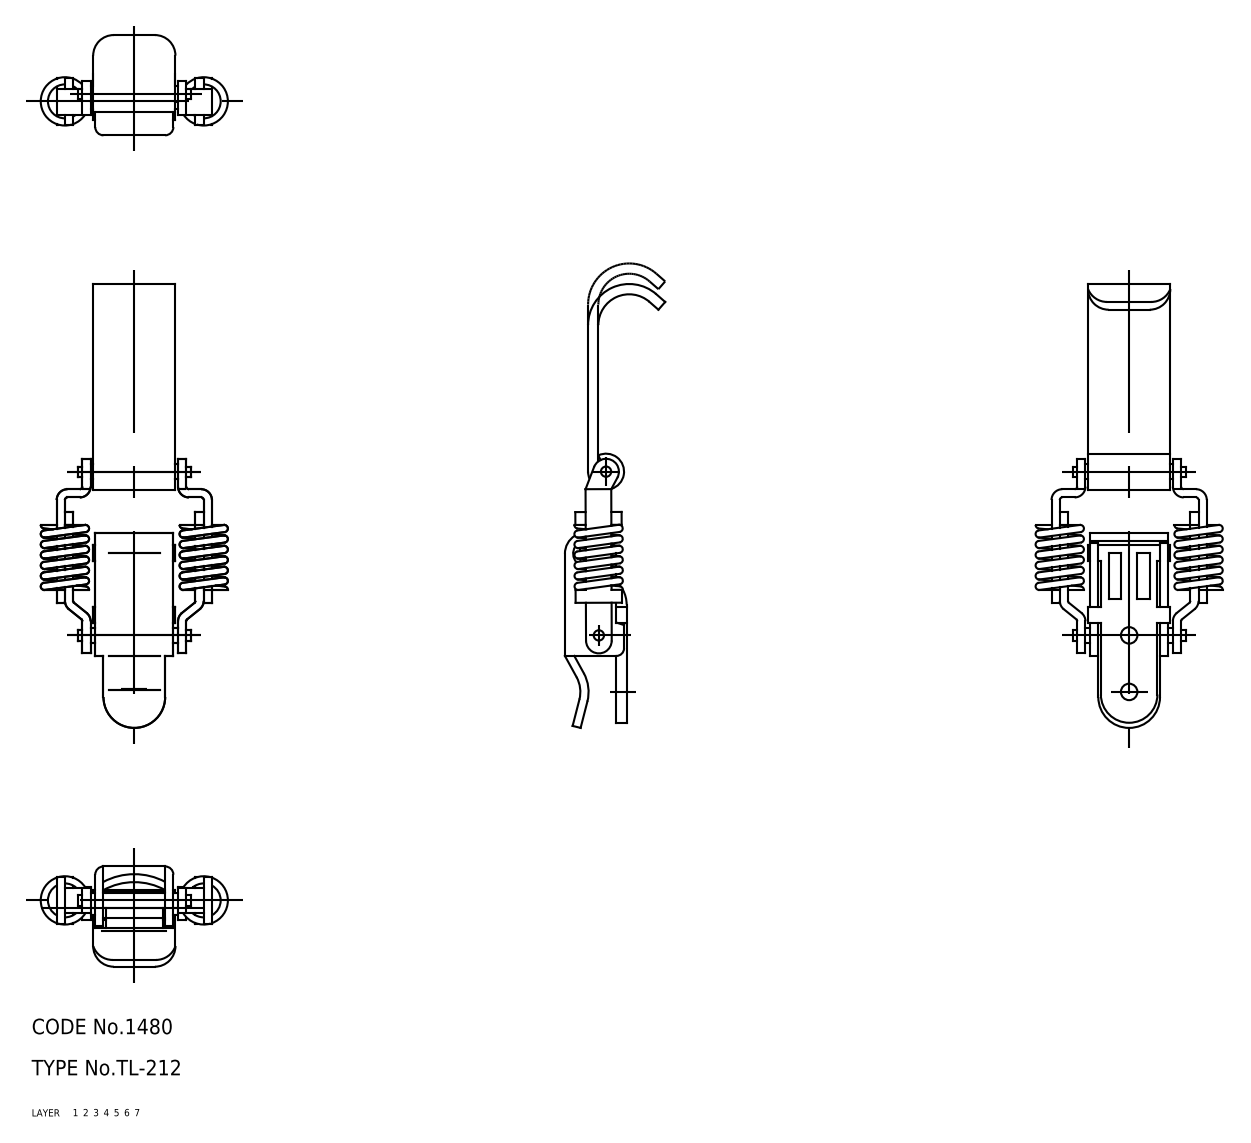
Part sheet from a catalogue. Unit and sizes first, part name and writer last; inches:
Units: inches
Overall size (bounding box): 3.287 × 1.433 × 0.768
Volume: 0.361 in³ · Surface area: 13.87 in²
Bodies: 11 solids, 276 faces (0 planar, 0 cylindrical, 276 other)
Part name (STEP PRODUCT): 67126152; 67126165; 67126178; 67126191 (+7 more)
STEP written by: CADfix (AUTOMOTIVE_DESIGN)
